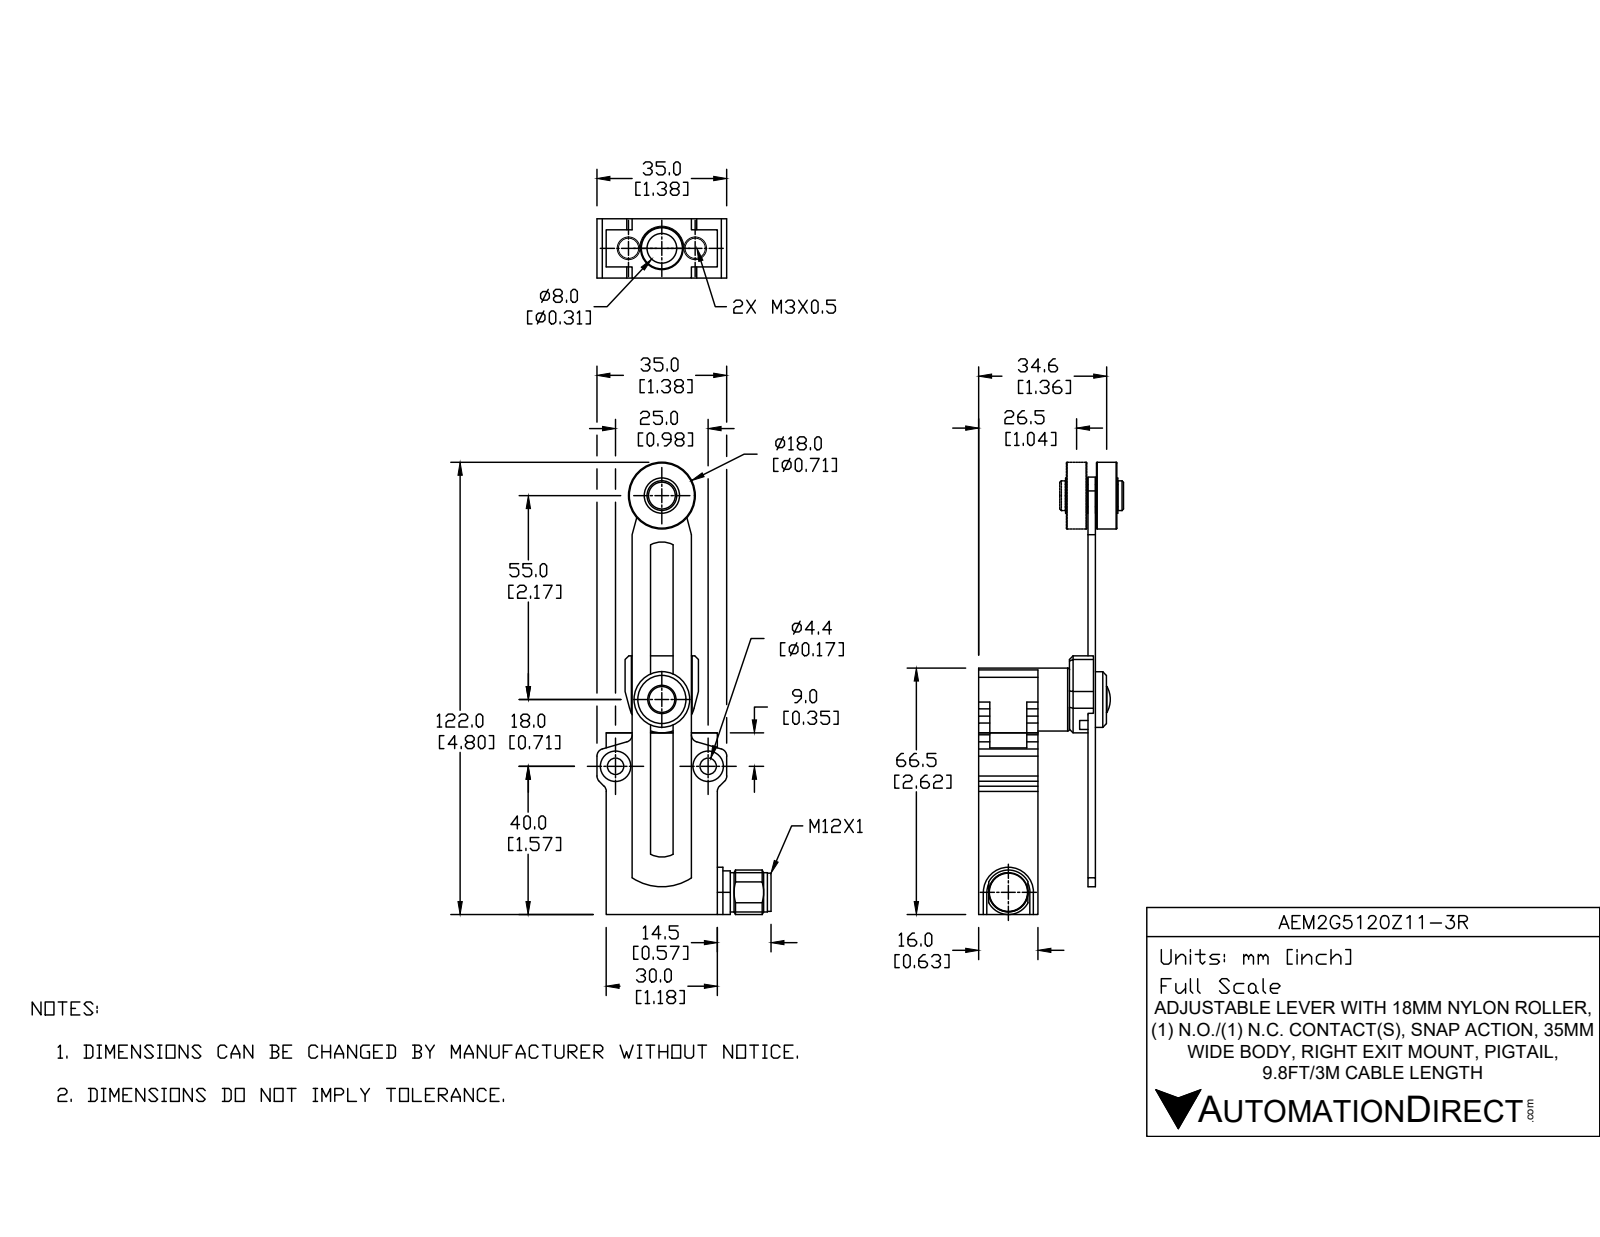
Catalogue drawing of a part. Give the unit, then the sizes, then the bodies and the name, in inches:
Units: inches
Overall size (bounding box): 5.06 × 1.831 × 1.587
Round holes (diameter × count): ⌀0.118 ×2, ⌀0.161 ×2, ⌀0.173 ×2, ⌀0.323 ×2, ⌀0.098 ×1, ⌀0.197 ×1, ⌀0.224 ×1, ⌀0.24 ×1, ⌀0.299 ×1
Round bosses / shafts (diameter × count): ⌀0.709 ×1, ⌀0.622 ×1, ⌀0.591 ×1, ⌀0.472 ×1, ⌀0.417 ×1, ⌀0.406 ×1, ⌀0.394 ×1, ⌀0.276 ×1
Partial cylindrical surfaces — rounded edges, fillets, slot ends (radius × count): R0.006 ×36, R0.079 ×10, R0.008 ×4, R0.047 ×4, R0.039 ×3, R0.256 ×3, R0.031 ×2, R0.059 ×1
Main face-to-face distances: 0.63, 1.291, 0.661, 1.181, 0.047, 0.614, 1.244, 2.047, 0.28, 0.902
Hole centre spacings: 0.863, 0.748, 0.984, 2.304, 3.052, 3.053
Volume: 2.15 in³ · Surface area: 25.01 in²
Bodies: 9 solids, 417 faces (196 planar, 152 cylindrical, 69 other)
Part name (STEP PRODUCT): AEM2G5120Z11MR
STEP written by: SolidWorks 2019 (AUTOMOTIVE_DESIGN)
